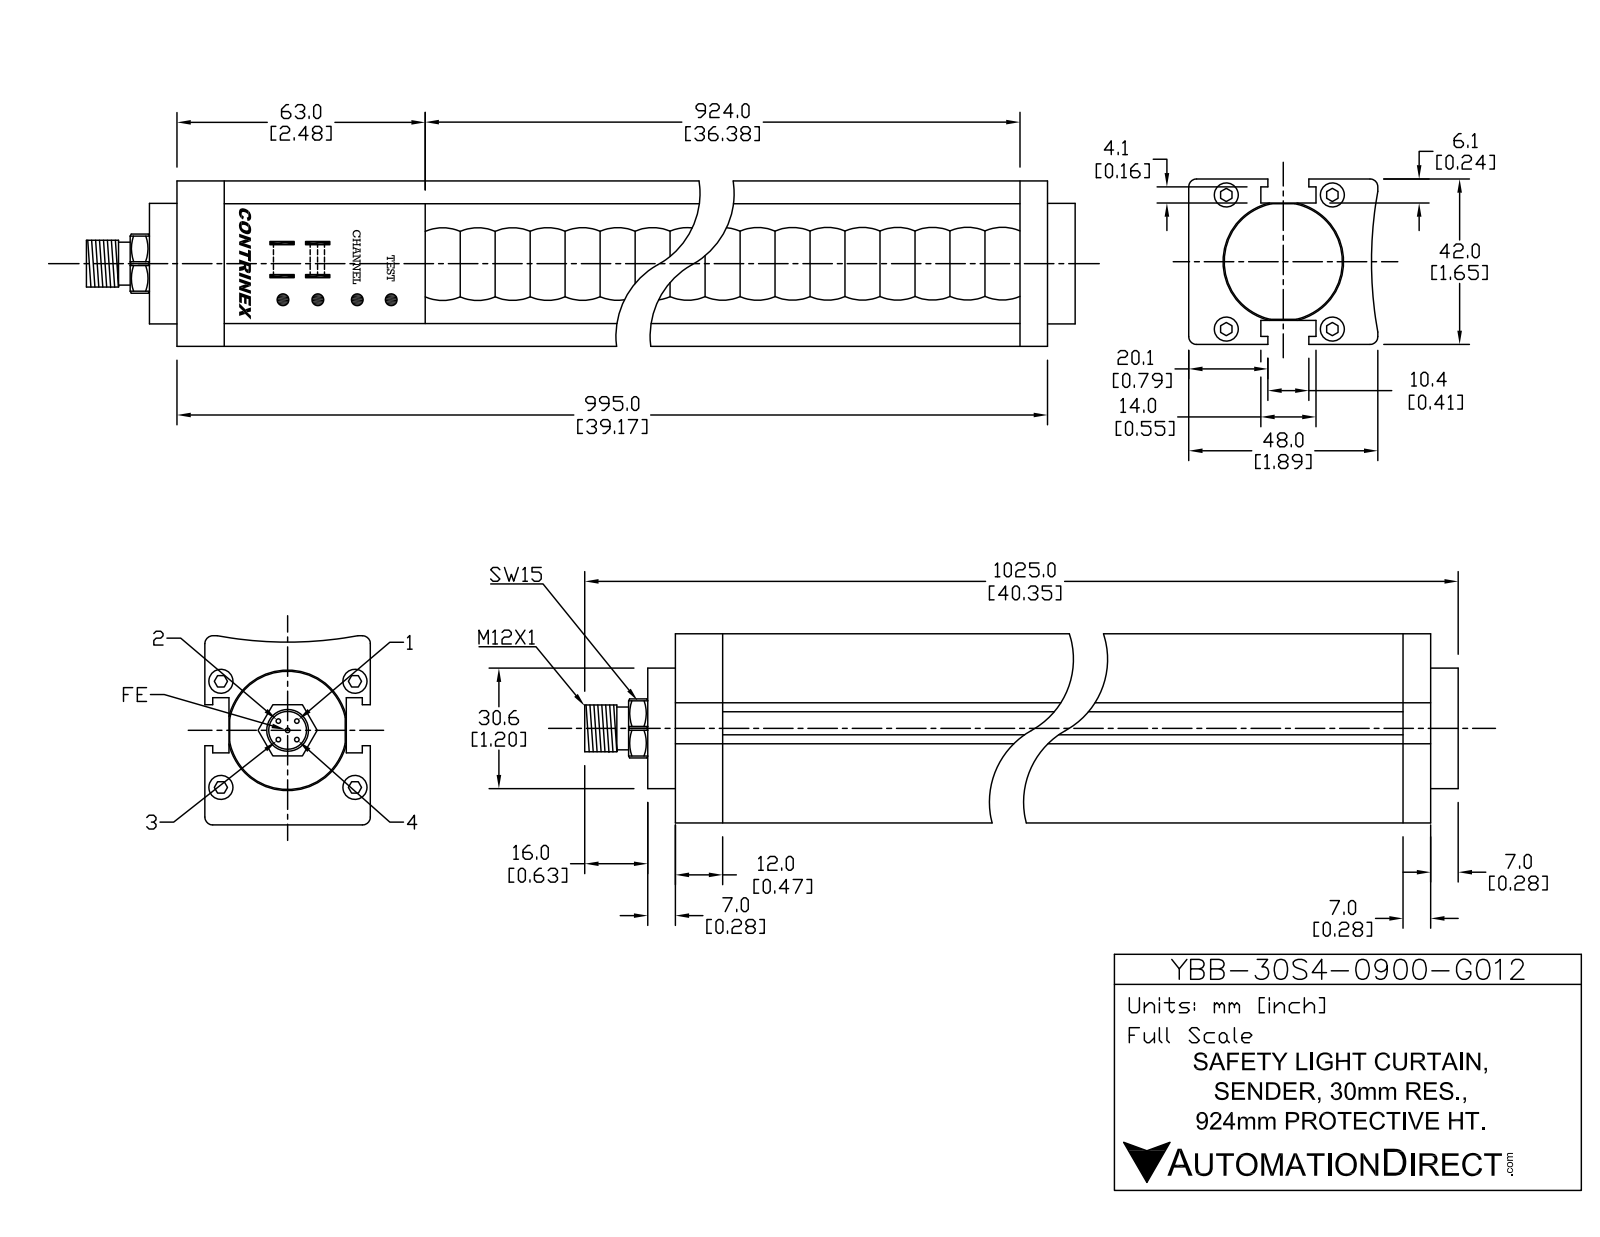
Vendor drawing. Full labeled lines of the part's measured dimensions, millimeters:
Part name (STEP PRODUCT): YBB-30S4-0900-G012
STEP written by: SolidWorks 2016 (AUTOMOTIVE_DESIGN)
Units: millimetres
Bodies: 19 solids, 440 faces (208 planar, 168 cylindrical, 64 other)
Overall size (bounding box): 1025 × 48 × 42
Volume: 1 792 000 mm³ · Surface area: 229 874 mm²
Round holes (diameter × count): ⌀6 ×4, ⌀8.5 ×1, ⌀32 ×1
Round bosses / shafts (diameter × count): ⌀1 ×5, ⌀5.5 ×4, ⌀30.6 ×1, ⌀12 ×1, ⌀10.5 ×1
Partial cylindrical surfaces — rounded edges, fillets, slot ends (radius × count): R1 ×48, R0.5 ×4, R0.55 ×2, R8.2 ×1, R100 ×1
Main face-to-face distances: 6.3, 35.7, 42, 29.4, 14, 17.2, 31.2, 15.7, 29.7, 46.9
Hole centre spacings: 21.04, 22.34, 26.9, 34, 43.35
